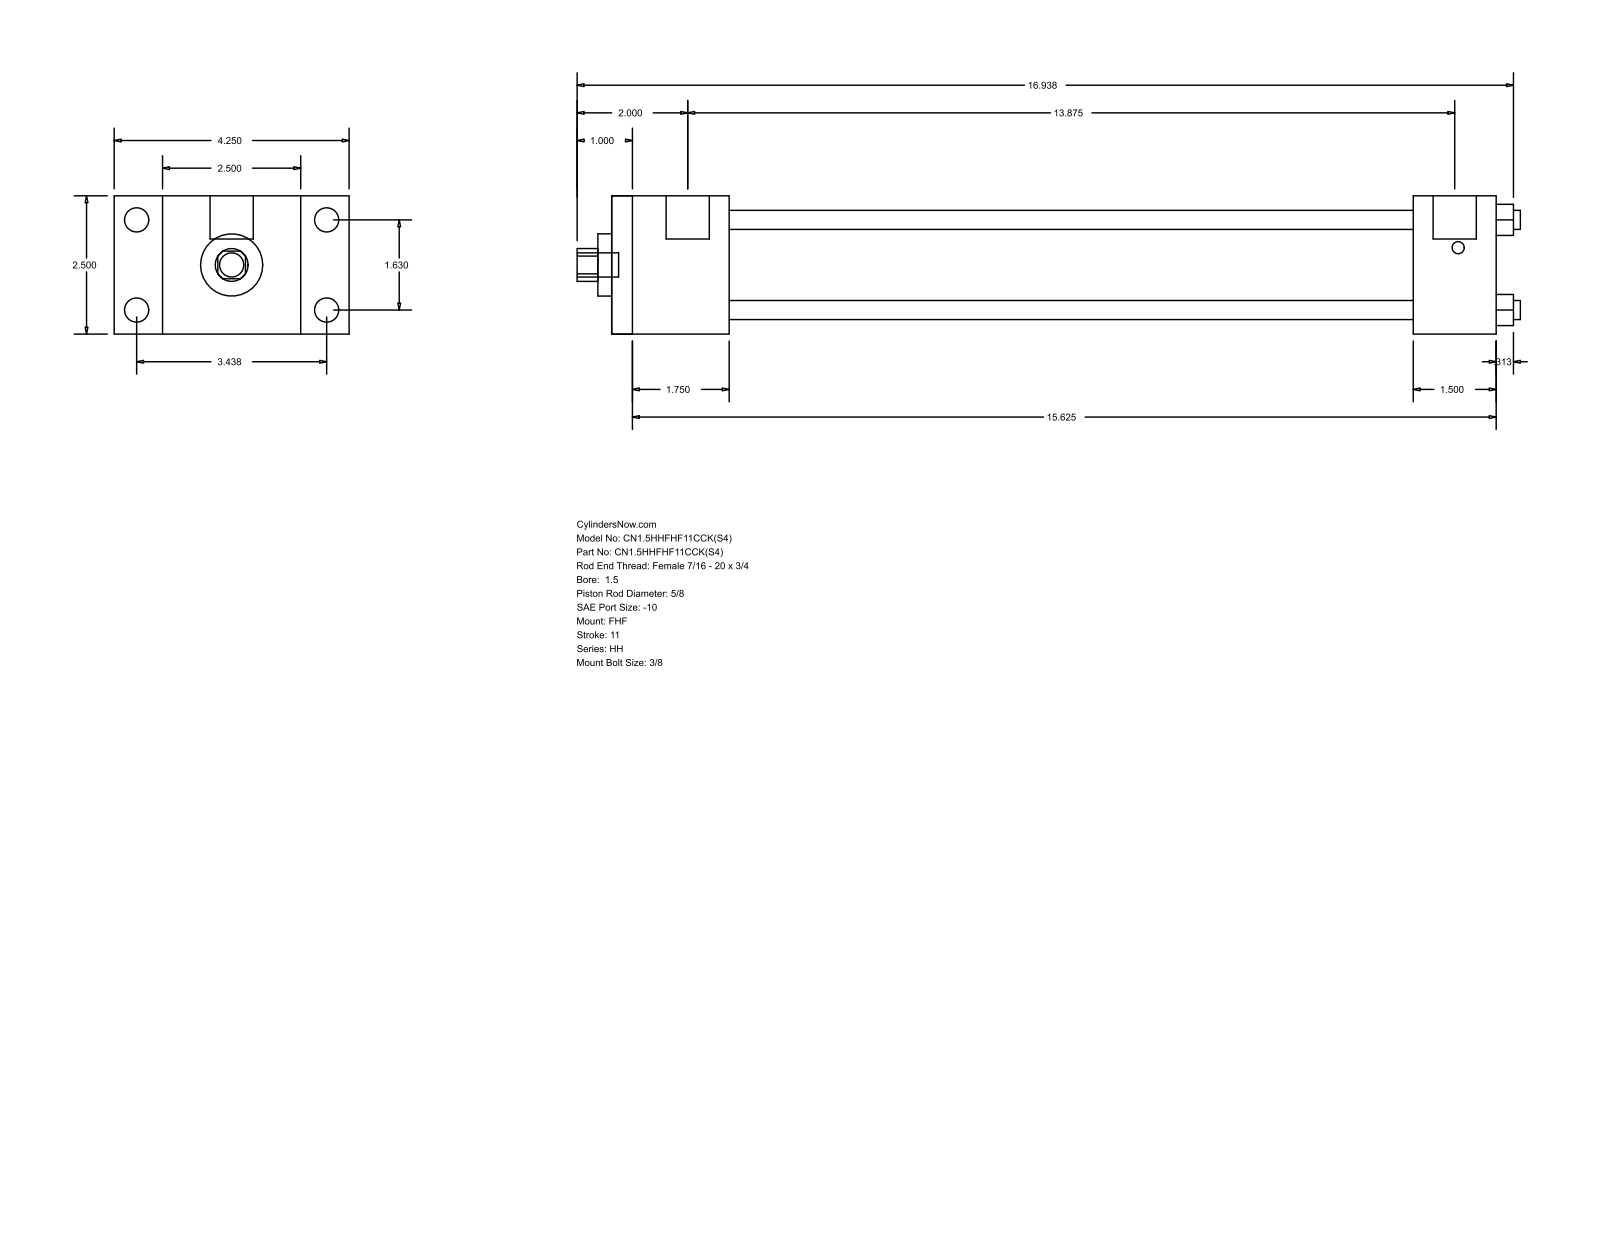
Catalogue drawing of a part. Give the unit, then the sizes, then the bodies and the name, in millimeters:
Units: millimetres
Overall size (bounding box): 433.39 × 107.95 × 63.5
Round holes (diameter × count): ⌀8.76 ×4, ⌀15.88 ×1, ⌀28.57 ×1, ⌀44.45 ×1
Round bosses / shafts (diameter × count): ⌀11.13 ×4, ⌀5.56 ×4, ⌀19.84 ×2, ⌀11.11 ×1
Partial cylindrical surfaces — rounded edges, fillets, slot ends (radius × count): R7.54 ×1
Main face-to-face distances: 63.5, 22.23, 85.73, 53.97, 107.96, 406.39, 352.42, 368.3, 314.33, 38.09
Hole centre spacings: 29.27, 41.4, 58.55
Bodies: 0 solids, 88 faces (60 planar, 28 cylindrical, 0 other)
Part name (STEP PRODUCT): HH_FHF__0150_0.625
STEP written by: GSSL Pune (CONFIG_CONTROL_DESIGN)
